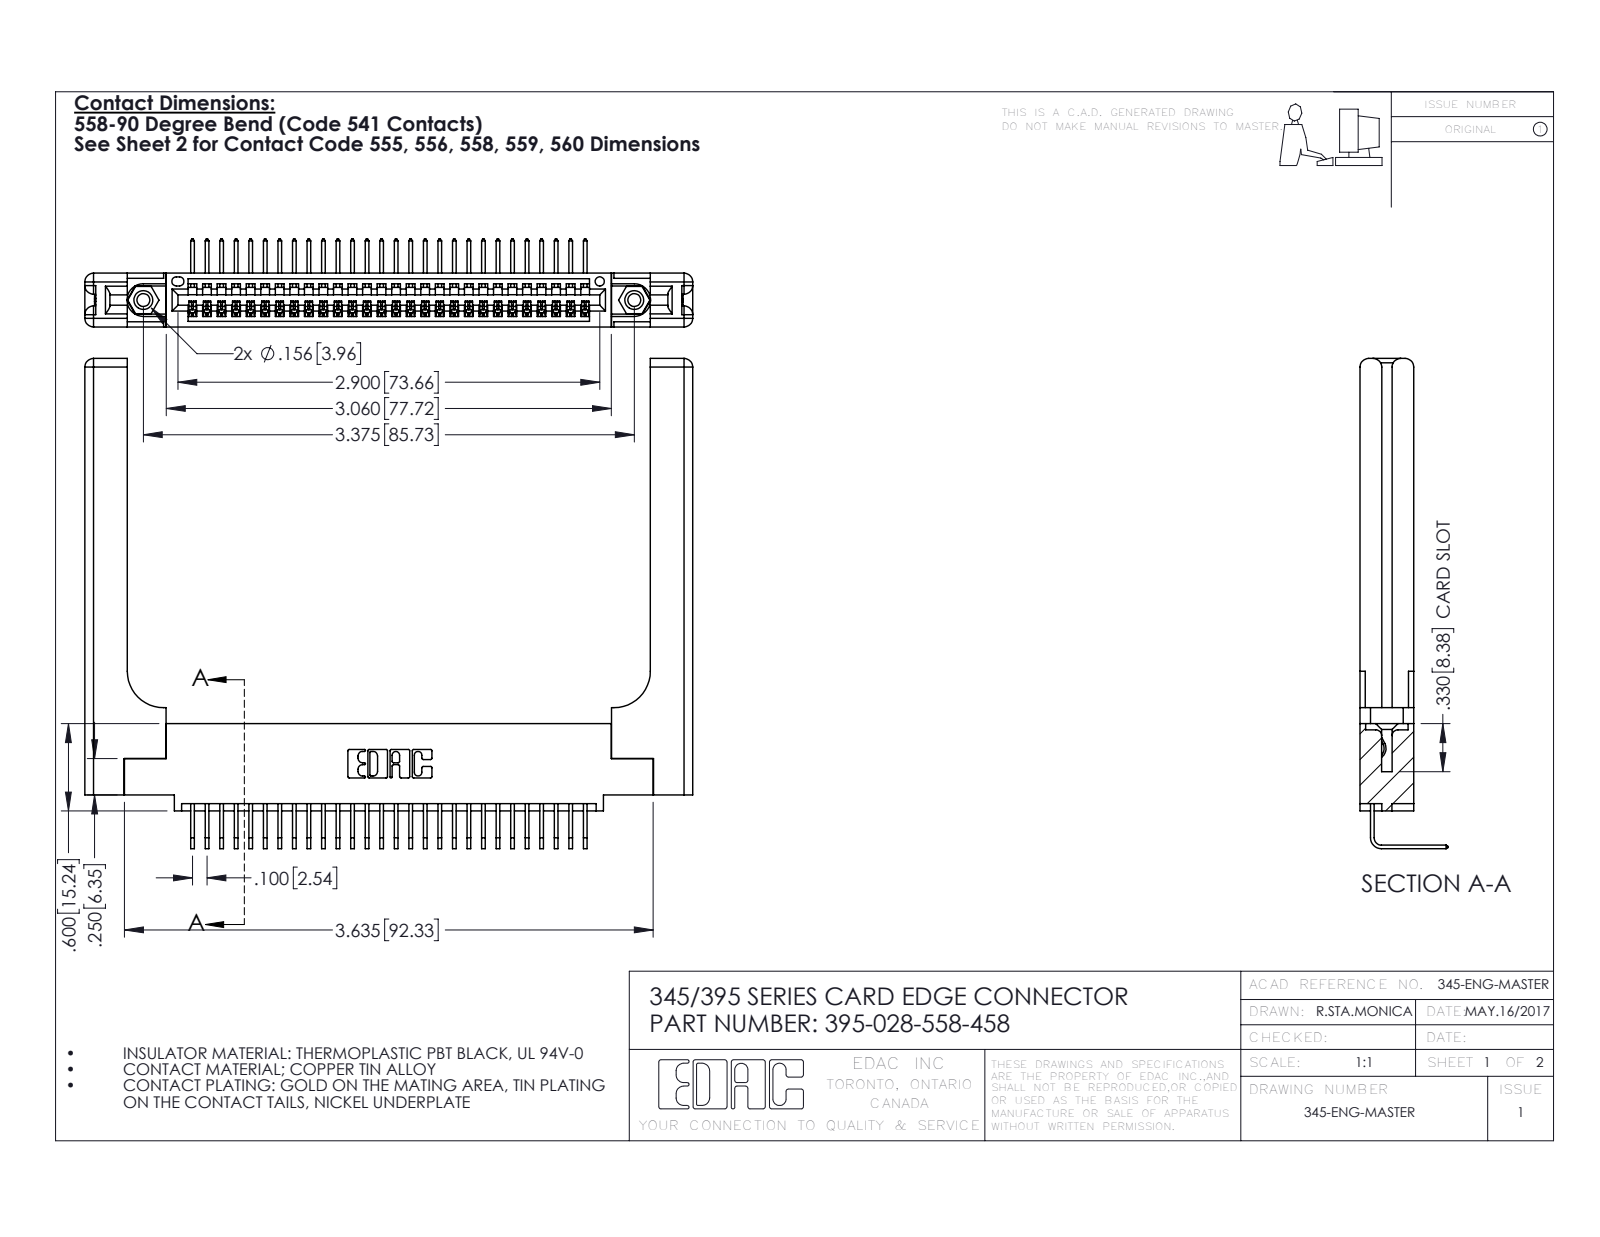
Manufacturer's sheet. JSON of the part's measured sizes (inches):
{"part_name": "345-250-001_345-250-001-102; 345-292-001_558 Tail - 2; 395-028-558-458; 345-220-058_345-220-058 (+1 more)", "step_written_by": "SolidWorks 2016 (CONFIG_CONTROL_DESIGN)", "units": "inches", "bodies": {"solids": 33, "faces": 2066, "planar": 1408, "cylindrical": 598, "other": 60}, "overall_size": [4.179, 3.369, 0.605], "volume_in3": 1.128, "surface_area_in2": 29.48, "round_holes": [[0.089, 2], [0.125, 2], [0.156, 2], [0.064, 1]], "round_bosses_or_shafts": [[0.155, 2]], "partial_cylinders_radius": [[0.006, 56], [0.01, 22], [0.06, 16], [0.007, 6], [0.031, 6], [0.026, 3], [0.03, 2], [0.031, 2]], "face_to_face_distances": [0.37, 0.072, 0.298, 0.148, 0.15, 0.098, 0.272, 0.025, 0.2, 0.077], "hole_center_spacings": [0.27, 3.14, 3.375]}
